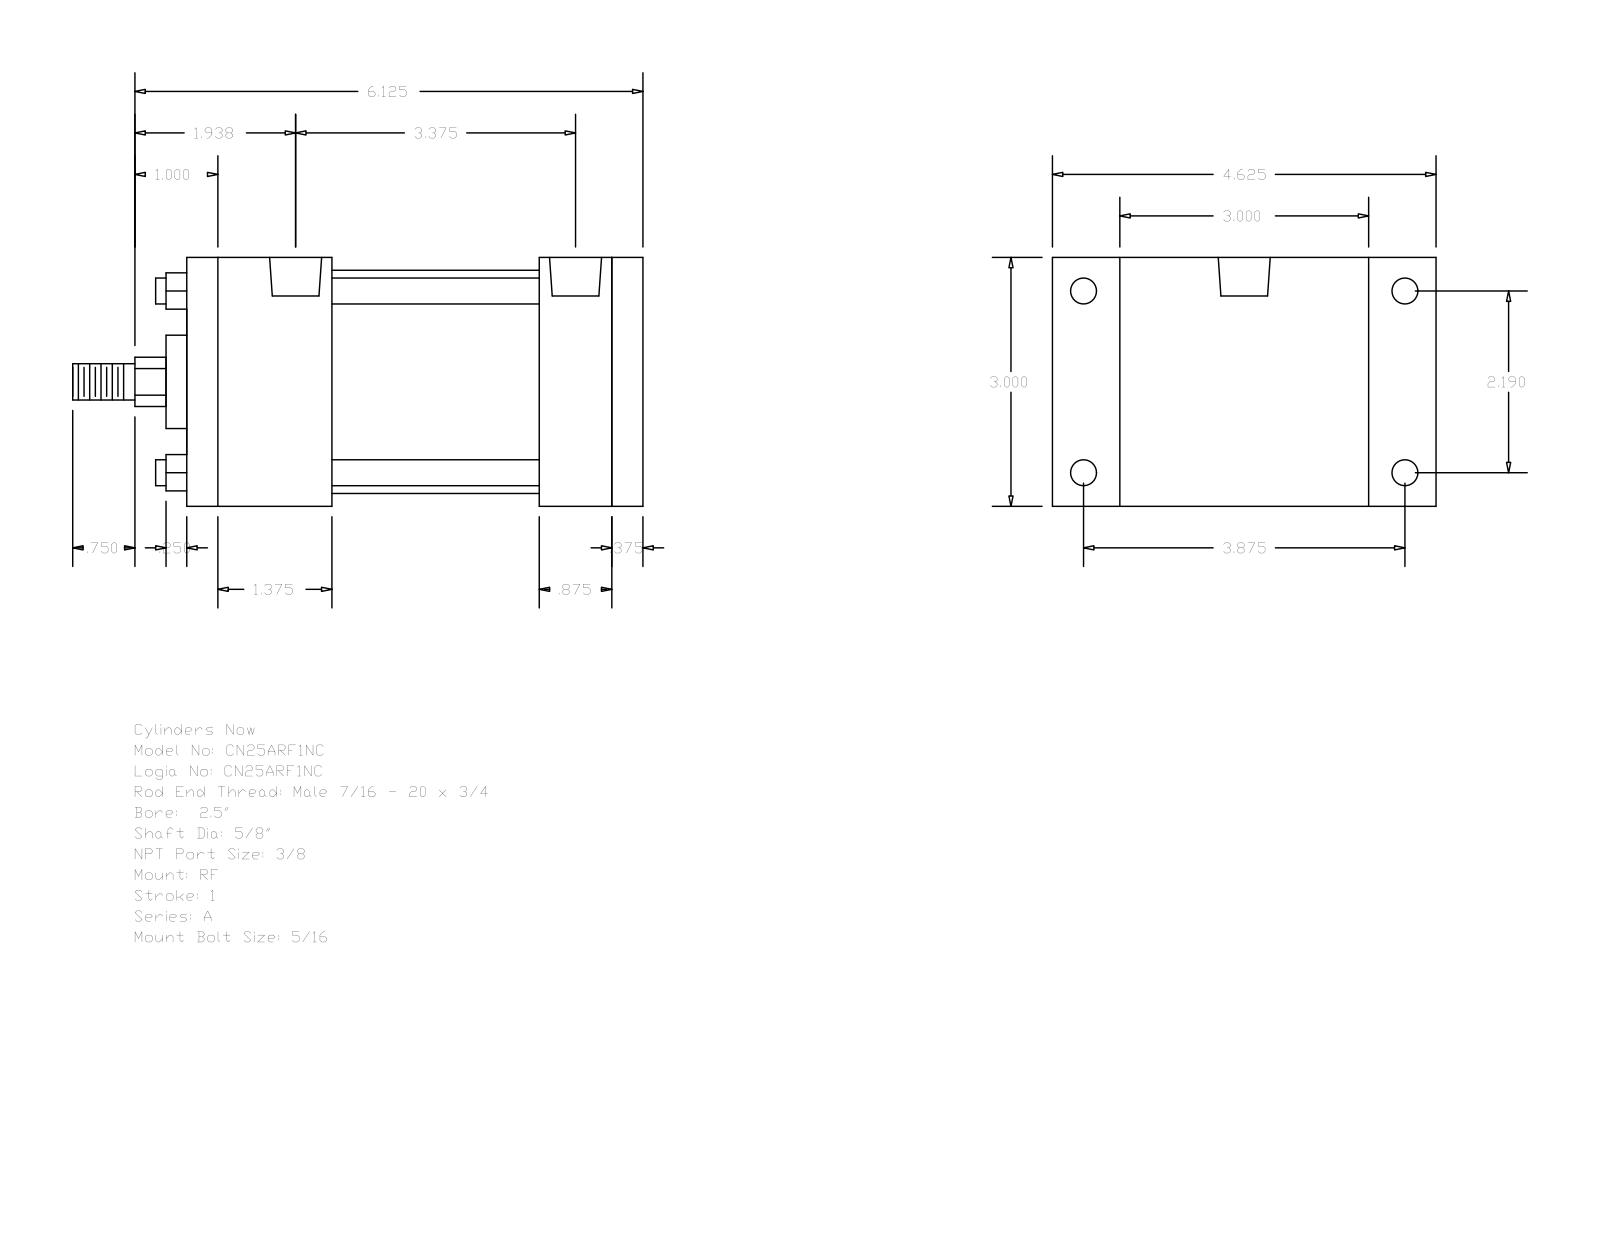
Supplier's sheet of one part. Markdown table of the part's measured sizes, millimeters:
| quantity | value |
| --- | --- |
| part name | A_RF__0250_0.625 |
| STEP written by | GSSL Pune (CONFIG_CONTROL_DESIGN) |
| units | millimeters |
| bodies | 0 solids, 92 faces (64 planar, 28 cylindrical, 0 other) |
| overall size | 174.62 × 117.47 × 76.2 |
| round holes (diameter × count) | 5.56 × 4, 7.94 × 4, 15.93 × 2 |
| round bosses / shafts (diameter × count) | 7.94 × 4, 68.33 × 1, 28.57 × 1, 15.88 × 1, 11.11 × 1 |
| partial cylindrical surfaces (radius × count) | 7.54 × 1 |
| main face-to-face distances | 76.2, 139.69, 130.17, 9.52, 44.45, 107.95, 63.5, 85.72, 95.24, 22.22 |
| hole center spacings | 2.38, 55.62, 88.11, 90.49, 98.42, 113.05, 85.73 |
